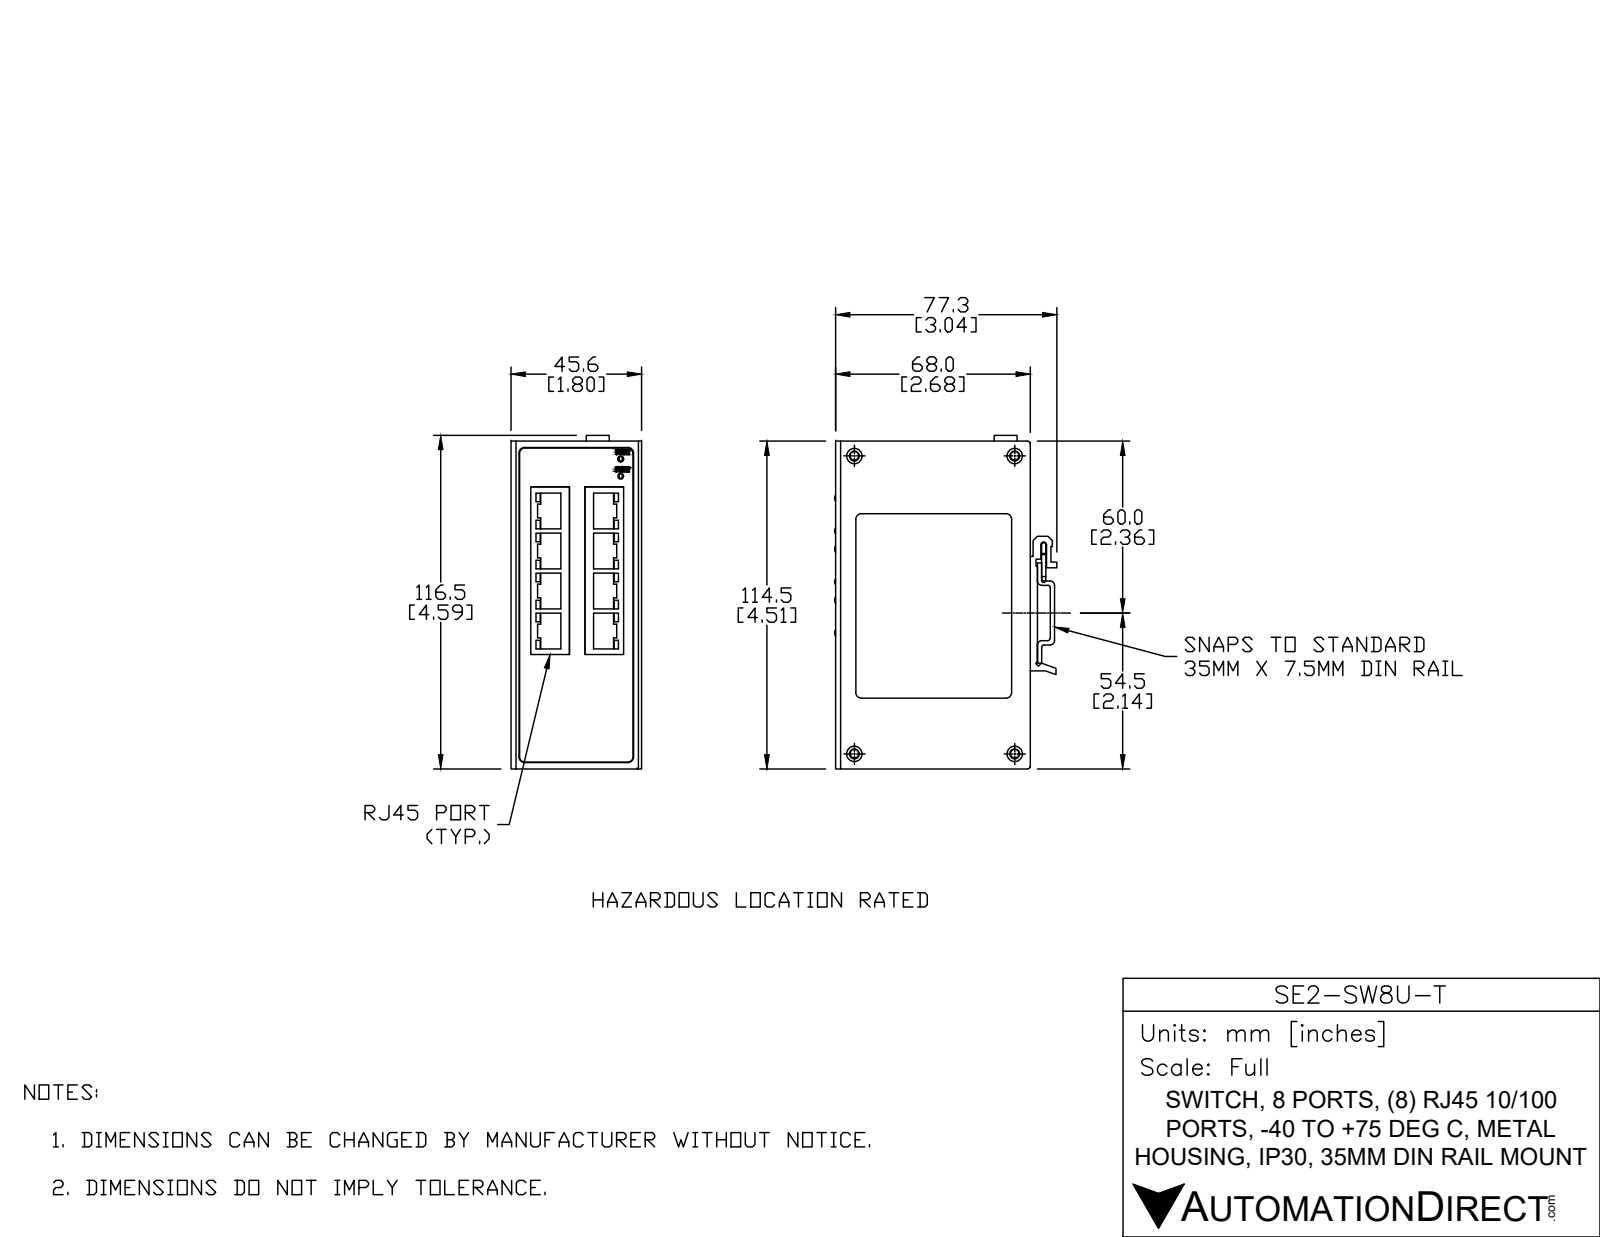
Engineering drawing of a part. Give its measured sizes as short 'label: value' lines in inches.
name: SE2-SW8U-T
written by: SolidWorks 2017 (AUTOMOTIVE_DESIGN)
unit: in
bodies: 14 solids, 1327 faces (991 planar, 291 cylindrical, 45 other)
size: 4.951 × 3.047 × 1.795
volume: 5.556 in³; area: 169.6 in²
holes: 6× ⌀0.11, 6× ⌀0.118, 4× ⌀0.051, 4× ⌀0.122, 4× ⌀0.15, 2× ⌀0.138, 2× ⌀0.157, 1× ⌀0.079, 1× ⌀0.181
bosses: 6× ⌀0.118, 4× ⌀0.197, 4× ⌀0.142, 4× ⌀0.051, 4× ⌀0.024, 1× ⌀0.315, 1× ⌀0.157
rounds: 96× R0.024, 8× R0.079, 8× R0.118, 6× R0.041, 5× R0.039, 4× R0.012, 4× R0.112, 4× R0.113
face distances: 0.039, 0.02, 1.756, 1.736, 0.059, 1.717, 2.618, 4.449, 0.701, 1.795
hole spacings: 0.546, 0.2, 0.866, 0.203, 0.4, 0.4, 0.581, 0.583
